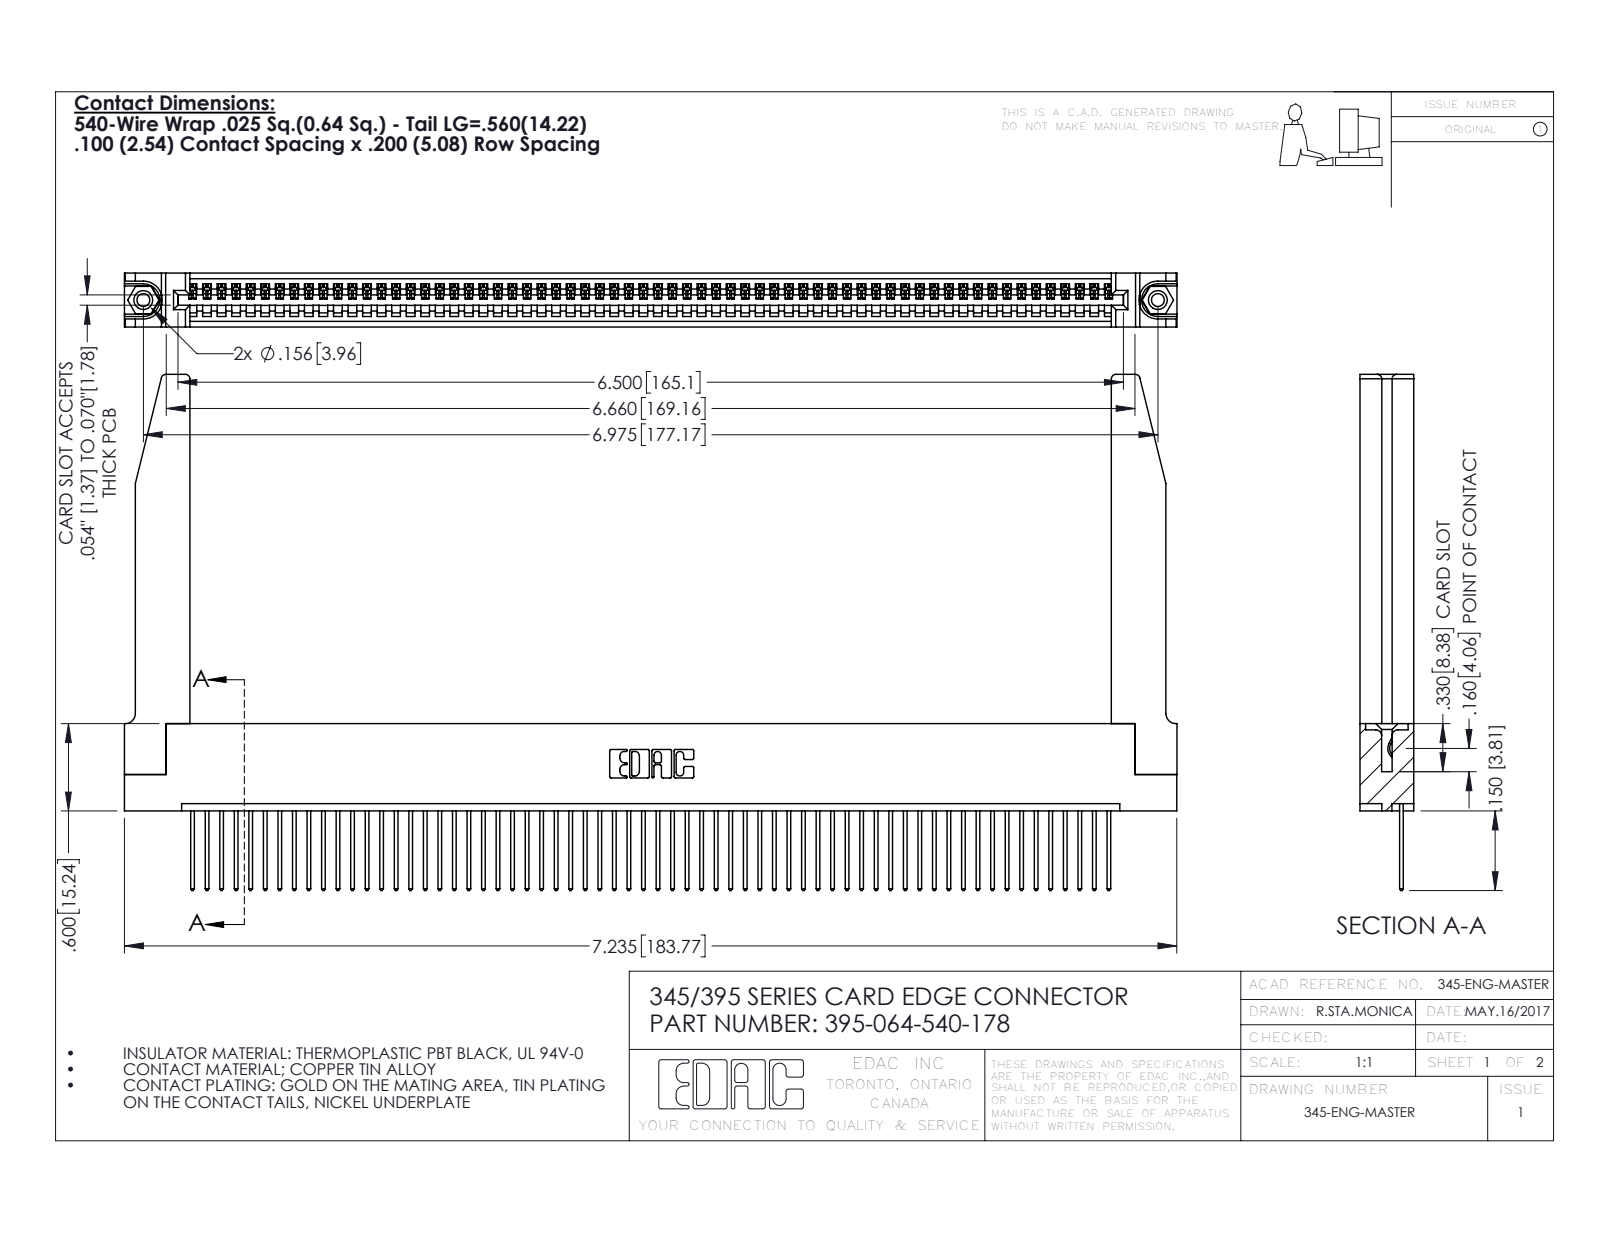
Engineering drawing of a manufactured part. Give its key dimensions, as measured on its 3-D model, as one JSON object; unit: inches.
{"part_name": "345-250-001_345-250-001-102; 345-292-001_345-293-140; 345 Part_Flush Mounting Lugs - 0.156 Dia-TH; 395-064-540-178 (+1 more)", "step_written_by": "SolidWorks 2016 (CONFIG_CONTROL_DESIGN)", "units": "inches", "bodies": {"solids": 69, "faces": 4072, "planar": 2782, "cylindrical": 1238, "other": 52}, "overall_size": [7.236, 3.547, 0.37], "volume_in3": 1.556, "surface_area_in2": 48.55, "round_holes": [[0.089, 2], [0.125, 2], [0.156, 2], [0.064, 1]], "round_bosses_or_shafts": [[0.155, 2]], "partial_cylinders_radius": [[0.006, 128], [0.01, 128], [0.01, 22], [0.03, 8], [0.007, 6], [0.031, 6], [0.026, 3], [0.031, 2]], "face_to_face_distances": [0.072, 0.298, 0.37, 0.098, 0.272, 0.025, 0.2, 0.225, 0.148, 0.15], "hole_center_spacings": [0.27, 6.739, 6.975]}
